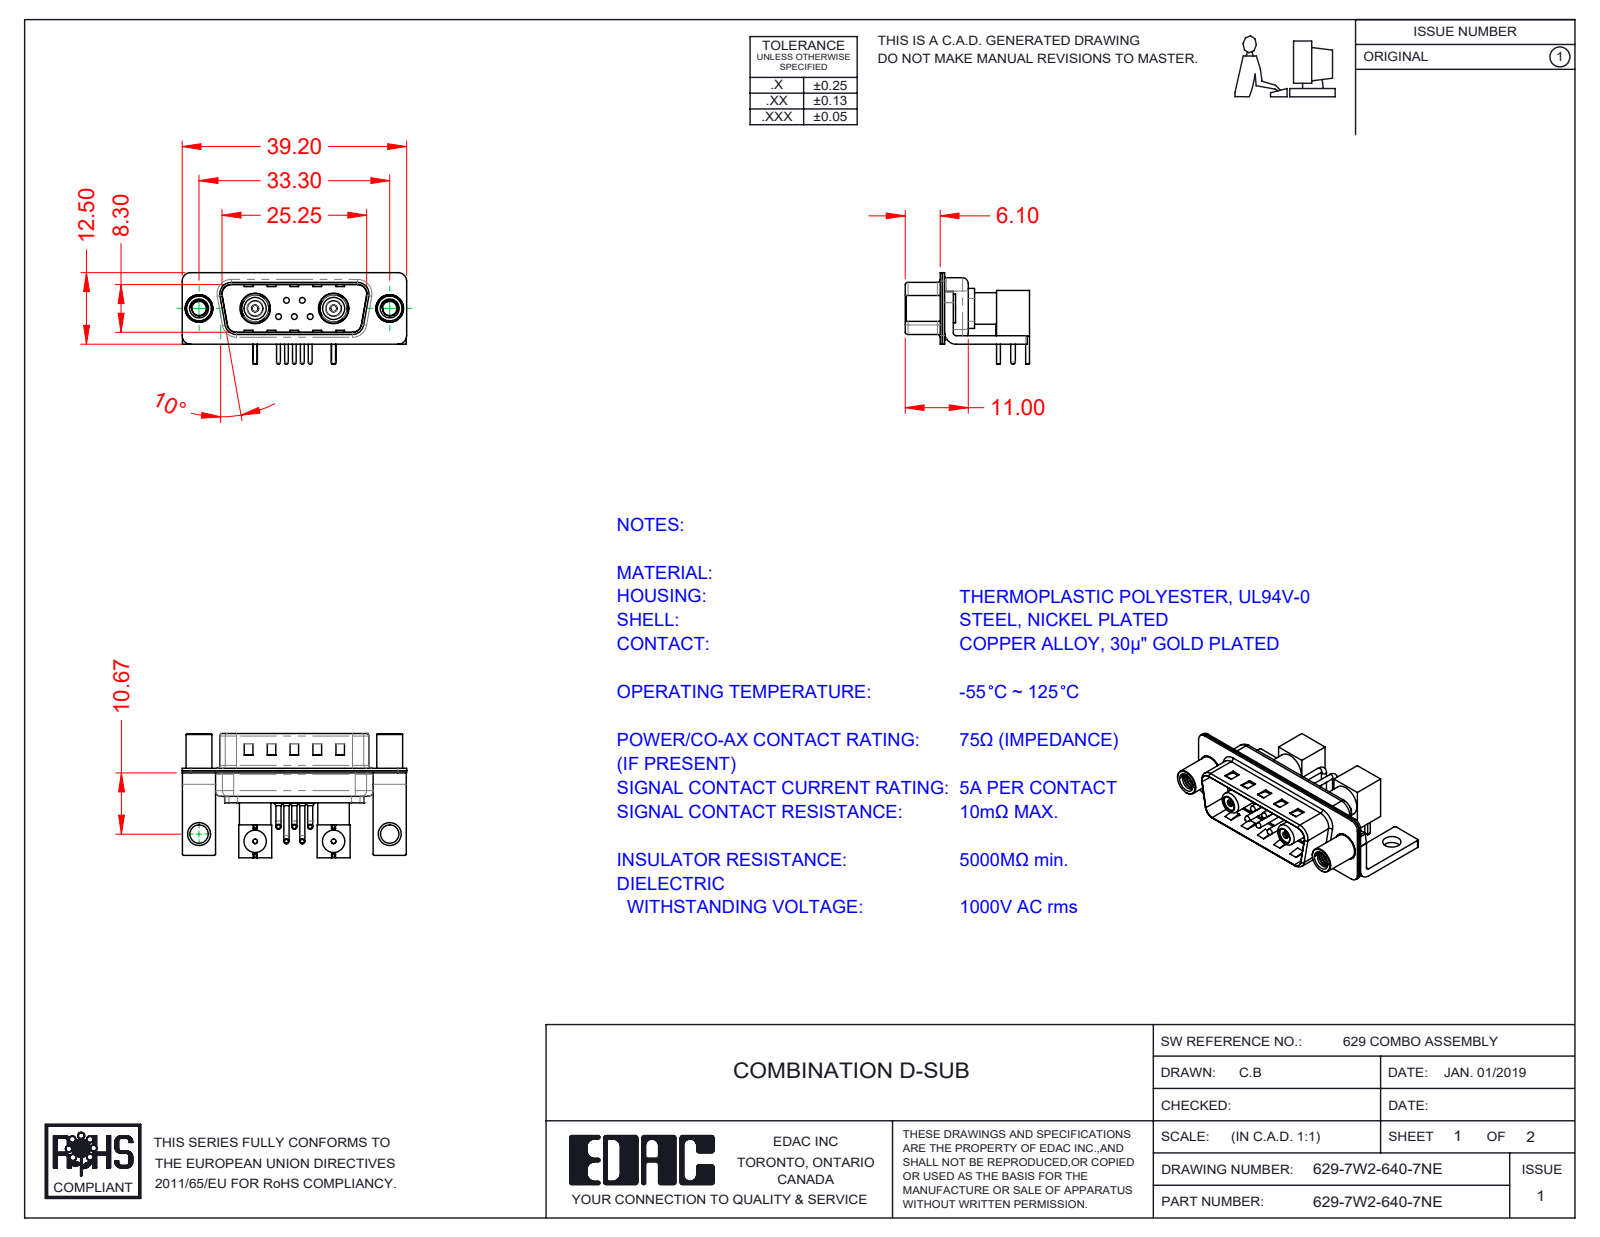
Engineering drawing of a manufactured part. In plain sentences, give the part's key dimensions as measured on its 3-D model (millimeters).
The part is named "629-7W2-640-7NE; Co-Ax Jack Assy_RA; Insulator Socket; 629Combo Shell Rear_15 Contacts (+8 more)". Its 3-D file was written by "SolidWorks 2020 (CONFIG_CONTROL_DESIGN)". It is 26 solids with 1292 faces: 595 planar, 519 cylindrical and 178 other. Overall it measures 39.2 by 21.71 by 16 millimeters. Its volume is 2 835 cubic millimeters and its surface area 7 708 square millimeters. Round holes: 7 of diameter 1.6, 5 of diameter 0.75, 5 of diameter 2, 4 of diameter 2.5, 2 of diameter 0.8, 2 of diameter 1.1, 2 of diameter 1.2, 2 of diameter 1.5, 2 of diameter 2.7, 2 of diameter 3.1, 2 of diameter 3.2, 2 of diameter 3.4. Round bosses or shafts: 10 of diameter 0.9, 5 of diameter 1.5, 5 of diameter 1, 5 of diameter 0.65, 4 of diameter 0.8, 2 of diameter 5.5, 2 of diameter 5.2, 2 of diameter 5. Partial cylindrical surfaces (rounded edges, fillets, slot ends): 16 of radius 0.25, 16 of radius 1.5, 13 of radius 2, 9 of radius 0.5, 8 of radius 1.6, 5 of radius 1.01, 4 of radius 0.6, 4 of radius 0.65. The main face-to-face distances are 0.4, 0.8, 1.5, 9.5, 9.1, 8.7, 5.75, 9.9, 0.35, 0.6. The hole center spacings are 13.7, 3.16, 9.88, 23.53, 2.77, 9.8, 23.5, 33.3.
